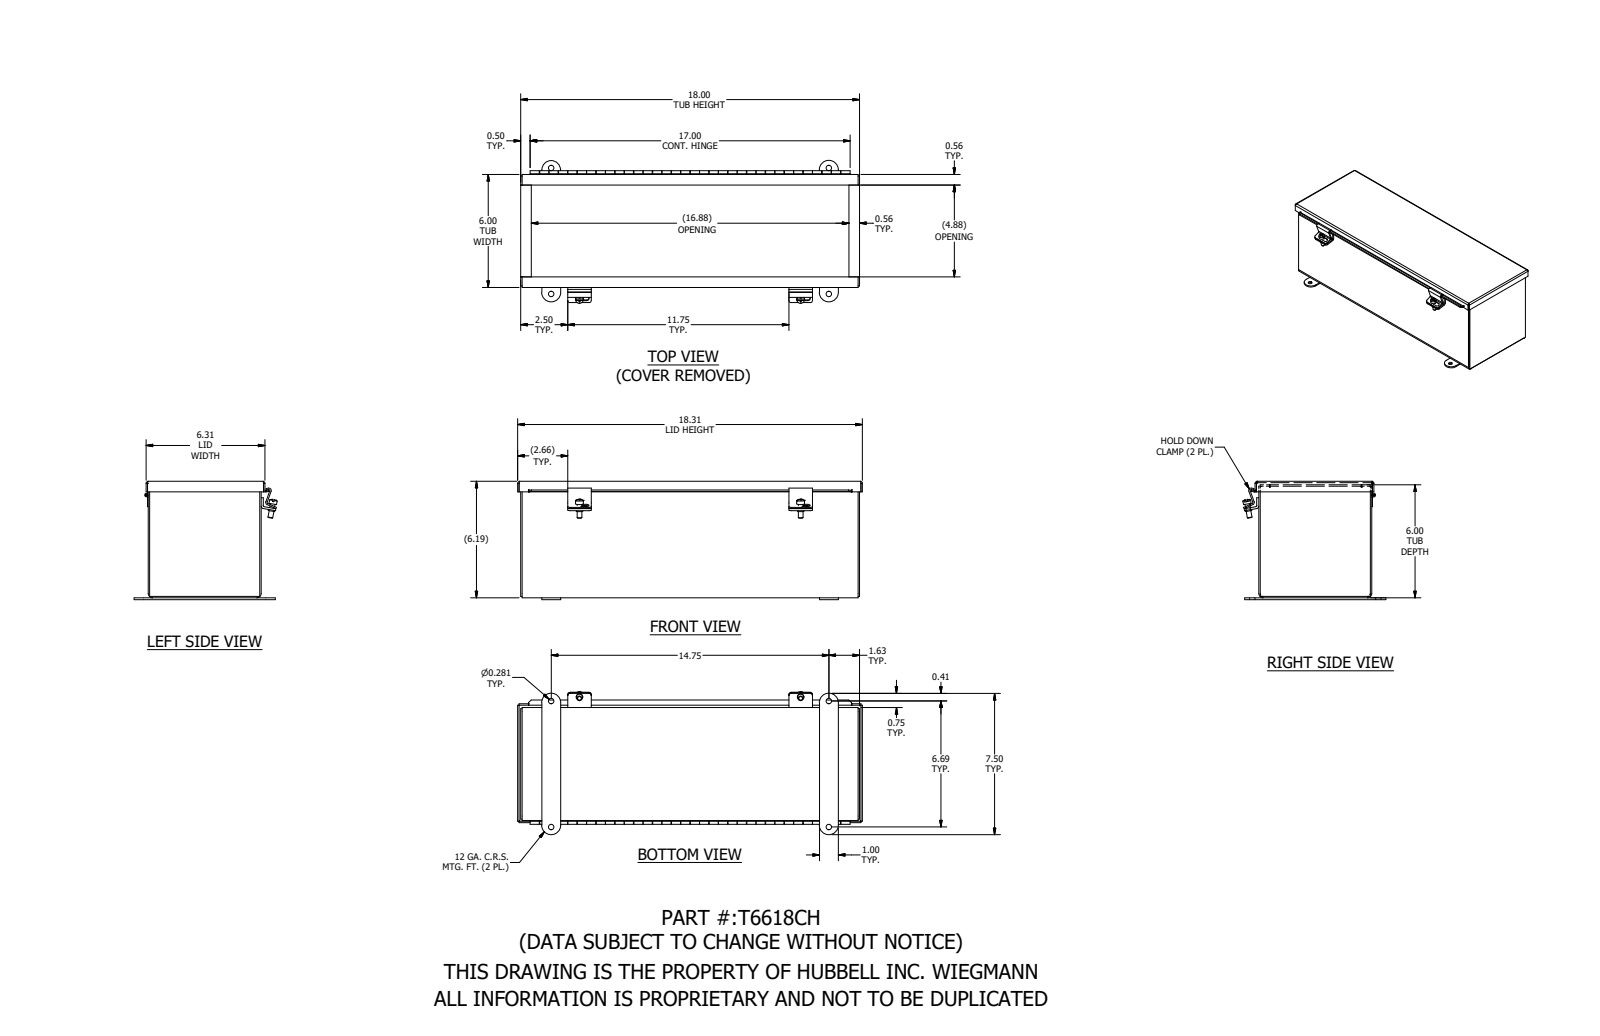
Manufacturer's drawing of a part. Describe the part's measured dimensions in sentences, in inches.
The part is named "T6618CH". Its 3-D file was written by "SolidWorks 2021 (AUTOMOTIVE_DESIGN)". It is 15 solids with 502 faces: 268 planar, 216 cylindrical and 18 other. Overall it measures 18.313 by 7.595 by 6.283 inches. Its volume is 43.7 cubic inches and its surface area 1 216 square inches. Round holes: 4 of diameter 0.281, 2 of diameter 0.196, 1 of diameter 0.116. Round bosses or shafts: 2 of diameter 0.41, 2 of diameter 0.344, 2 of diameter 0.25, 1 of diameter 0.2, 1 of diameter 0.1. Partial cylindrical surfaces (rounded edges, fillets, slot ends): 9 of radius 0.031, 9 of radius 0.105, 8 of radius 0.125, 4 of radius 0.133, 4 of radius 0.5, 3 of radius 0.063, 3 of radius 0.126, 2 of radius 0.156. The main face-to-face distances are 0.074, 5.926, 6.115, 6, 5.852, 6.189, 6.041, 17.926, 0.189, 17.852. The hole center spacings are 6.687, 14.75, 16.195, 11.75.
